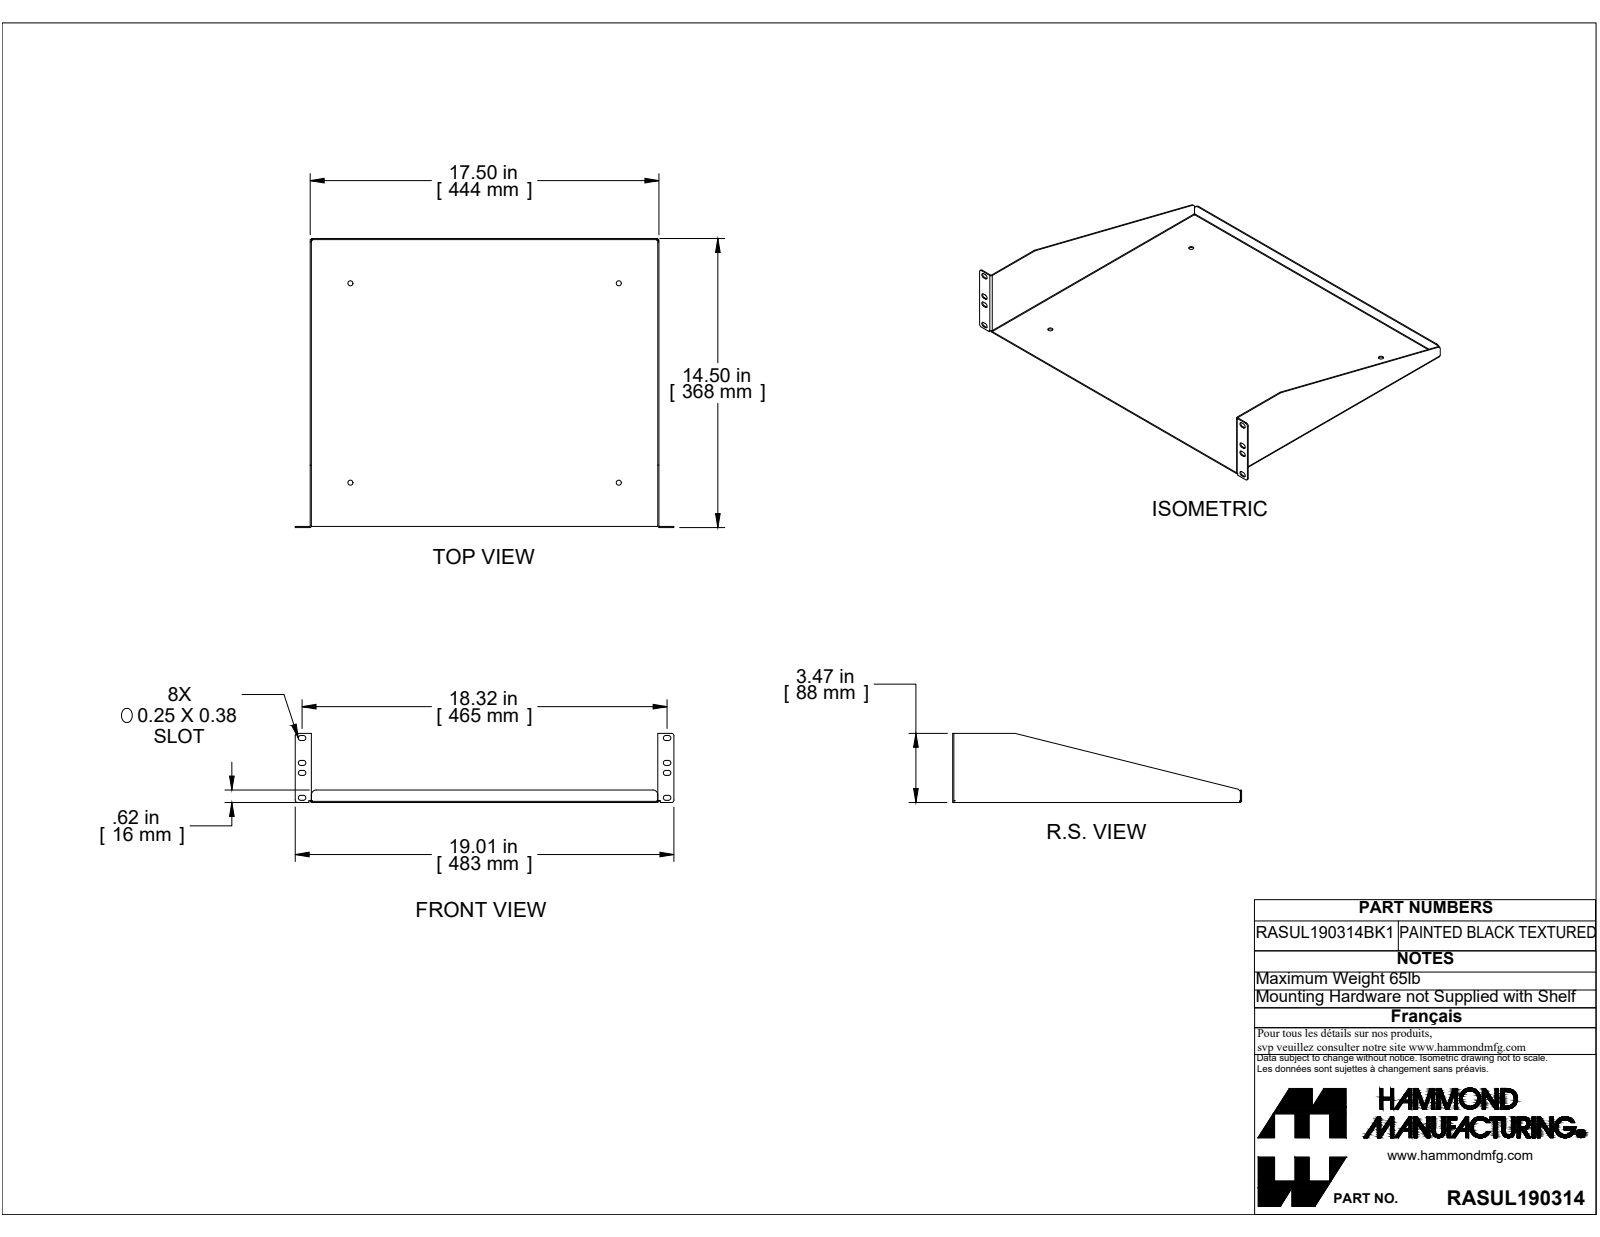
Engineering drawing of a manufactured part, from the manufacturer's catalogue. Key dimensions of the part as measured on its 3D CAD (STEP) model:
Part name (STEP PRODUCT): RASUL190314BK1
STEP written by: SolidWorks 2019 (CONFIG_CONTROL_DESIGN)
Units: inches
Bodies: 0 solids, 102 faces (58 planar, 40 cylindrical, 4 other)
Overall size (bounding box): 19.006 × 14.5 × 3.468
Round bosses / shafts (diameter × count): ⌀0.25 ×4
Partial cylindrical surfaces — rounded edges, fillets, slot ends (radius × count): R0.125 ×20, R0.029 ×5, R0.086 ×5, R0.055 ×3, R0.25 ×2
Main face-to-face distances: 0.057, 17.443, 17.386, 17.5, 14.386, 14.443, 0.057, 14.443, 14.5, 0.625
